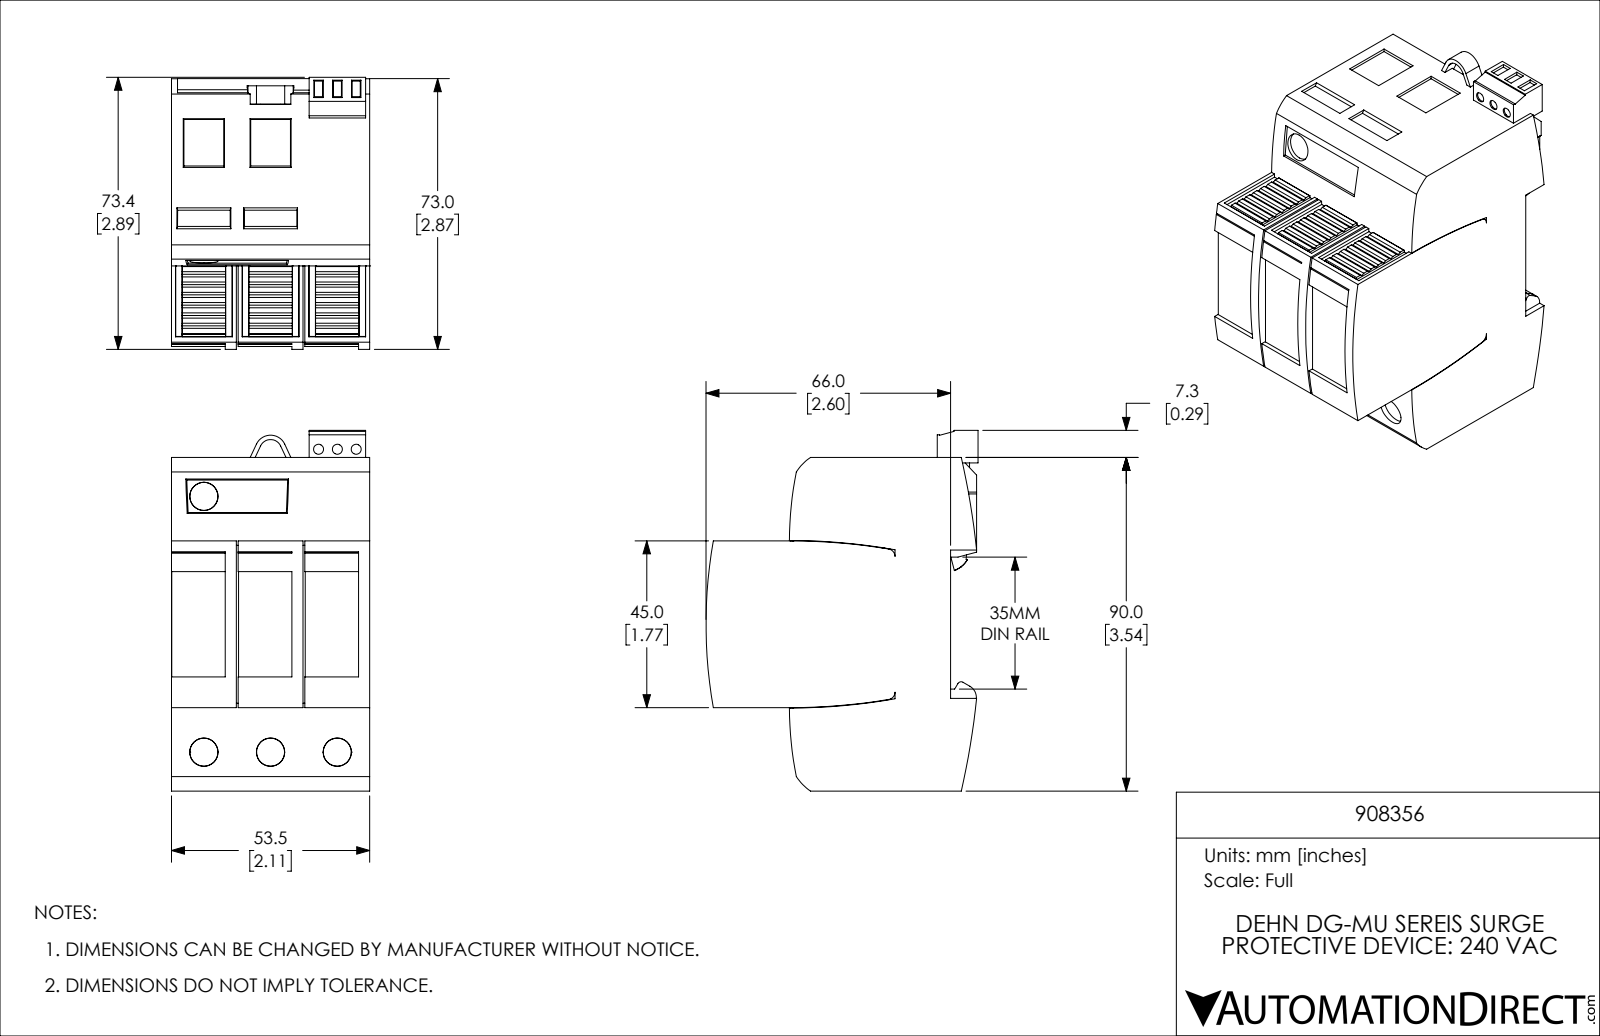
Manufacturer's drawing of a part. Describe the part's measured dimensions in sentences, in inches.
The part is named "908356". Its 3-D file was written by "SolidWorks 2019 (CONFIG_CONTROL_DESIGN)". It is 1 solid with 672 faces: 506 planar, 128 cylindrical and 38 other. Overall it measures 3.831 by 2.89 by 2.106 inches. Its volume is 16.59 cubic inches and its surface area 55.39 square inches. Round holes: 3 of diameter 0.106. Partial cylindrical surfaces (rounded edges, fillets, slot ends): 12 of radius 0.004, 12 of radius 0.047, 3 of radius 0.02, 2 of radius 0.008, 2 of radius 0.016, 2 of radius 0.03, 2 of radius 0.079, 2 of radius 0.079. The main face-to-face distances are 0.709, 2.106, 0.685, 0.689, 1.417, 1.398, 1.394, 3.543, 0.024, 2.518. The hole center spacings are 0.2, 0.4.
